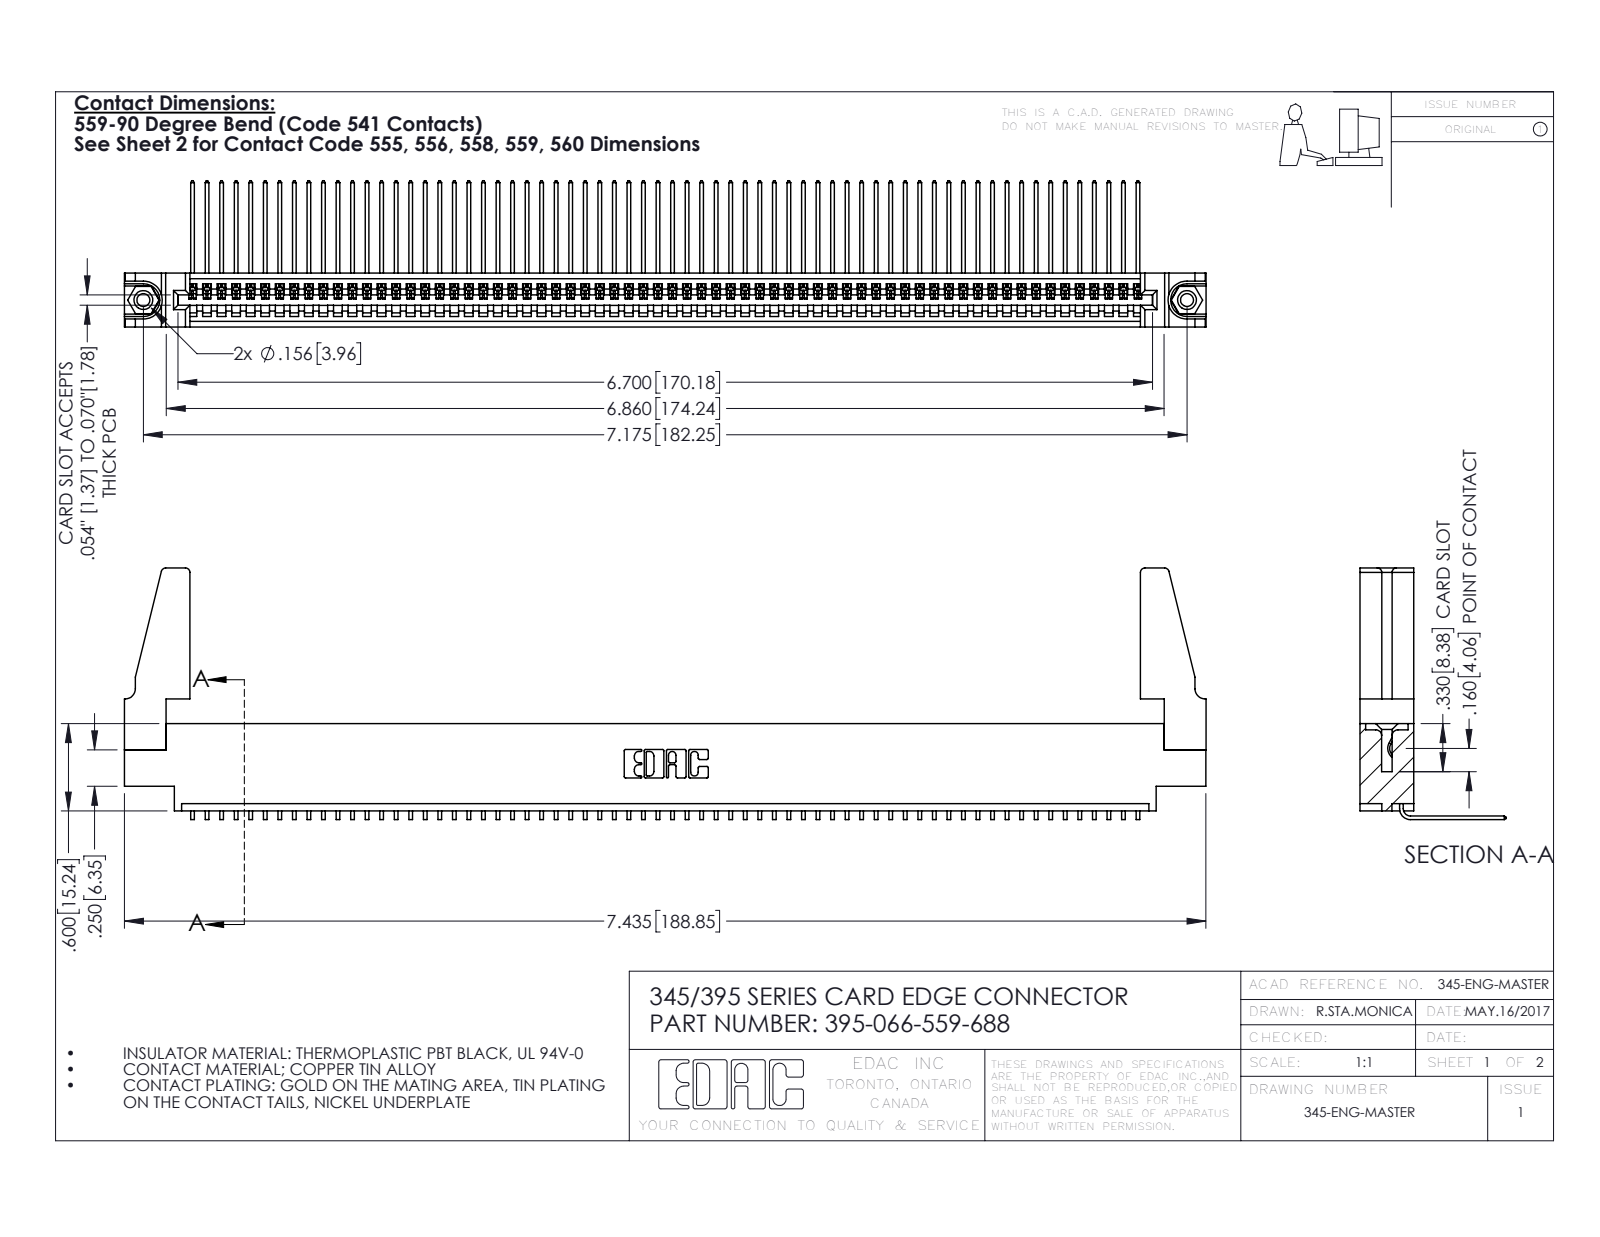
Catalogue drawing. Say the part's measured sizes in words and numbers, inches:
The part is named "345-292-001_558 559 Tail - 1; 345-220-078_345-220-088; 395-066-559-688; 345-250-001_345-250-001-102 (+1 more)". Its 3-D file was written by "SolidWorks 2016 (CONFIG_CONTROL_DESIGN)". It is 71 solids with 4214 faces: 2928 planar, 1270 cylindrical and 16 other. Overall it measures 7.436 by 1.729 by 1.005 inches. Its volume is 1.312 cubic inches and its surface area 45.13 square inches. Round holes: 2 of diameter 0.089, 2 of diameter 0.125, 2 of diameter 0.156, 1 of diameter 0.064. Round bosses or shafts: 2 of diameter 0.155. Partial cylindrical surfaces (rounded edges, fillets, slot ends): 132 of radius 0.006, 22 of radius 0.01, 8 of radius 0.03, 6 of radius 0.007, 6 of radius 0.031, 3 of radius 0.026, 2 of radius 0.031, 2 of radius 0.04. The main face-to-face distances are 0.072, 0.298, 0.37, 0.098, 0.272, 0.025, 0.2, 0.225, 0.175, 0.149. The hole center spacings are 0.27, 6.939, 7.175.
